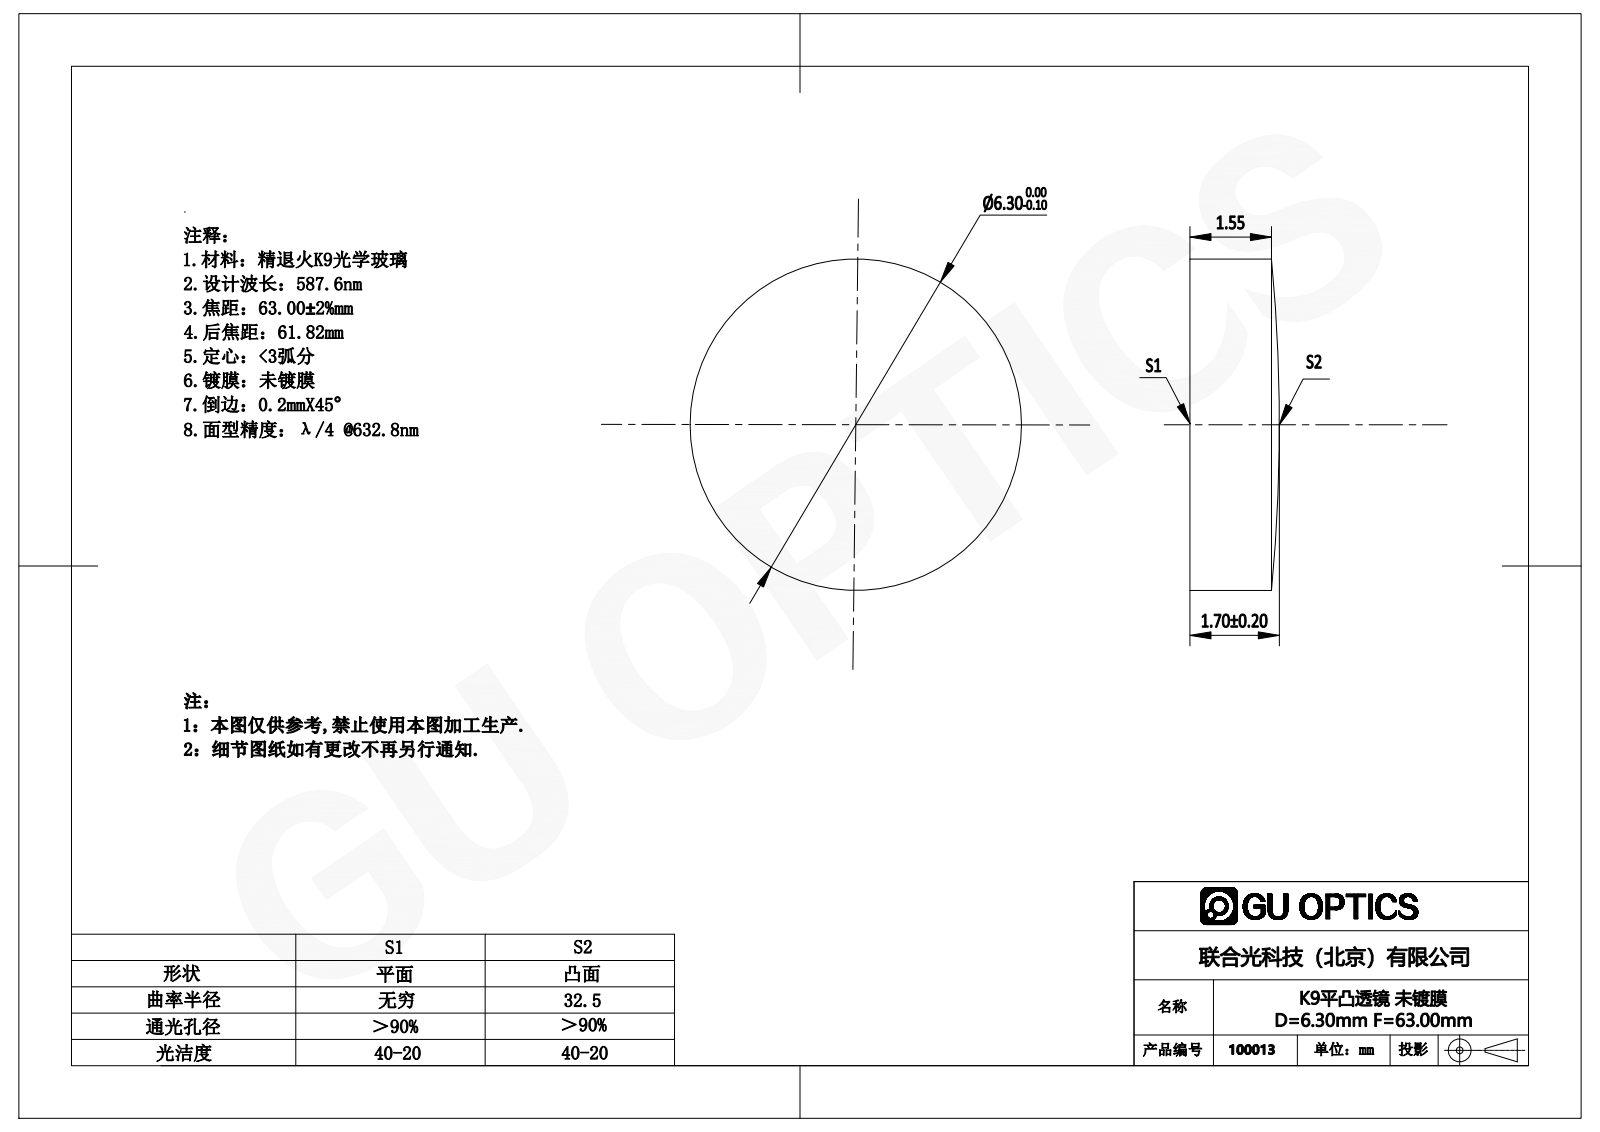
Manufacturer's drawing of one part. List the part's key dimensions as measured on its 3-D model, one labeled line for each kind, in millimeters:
Part name (STEP PRODUCT): 100013
STEP written by: SolidWorks 2016 (AUTOMOTIVE_DESIGN)
Units: millimetres
Bodies: 1 solid, 5 faces (1 planar, 2 cylindrical, 2 other)
Overall size (bounding box): 6.3 × 6.3 × 1.7
Volume: 51 mm³ · Surface area: 93 mm²
Round bosses / shafts (diameter × count): ⌀6.3 ×1
